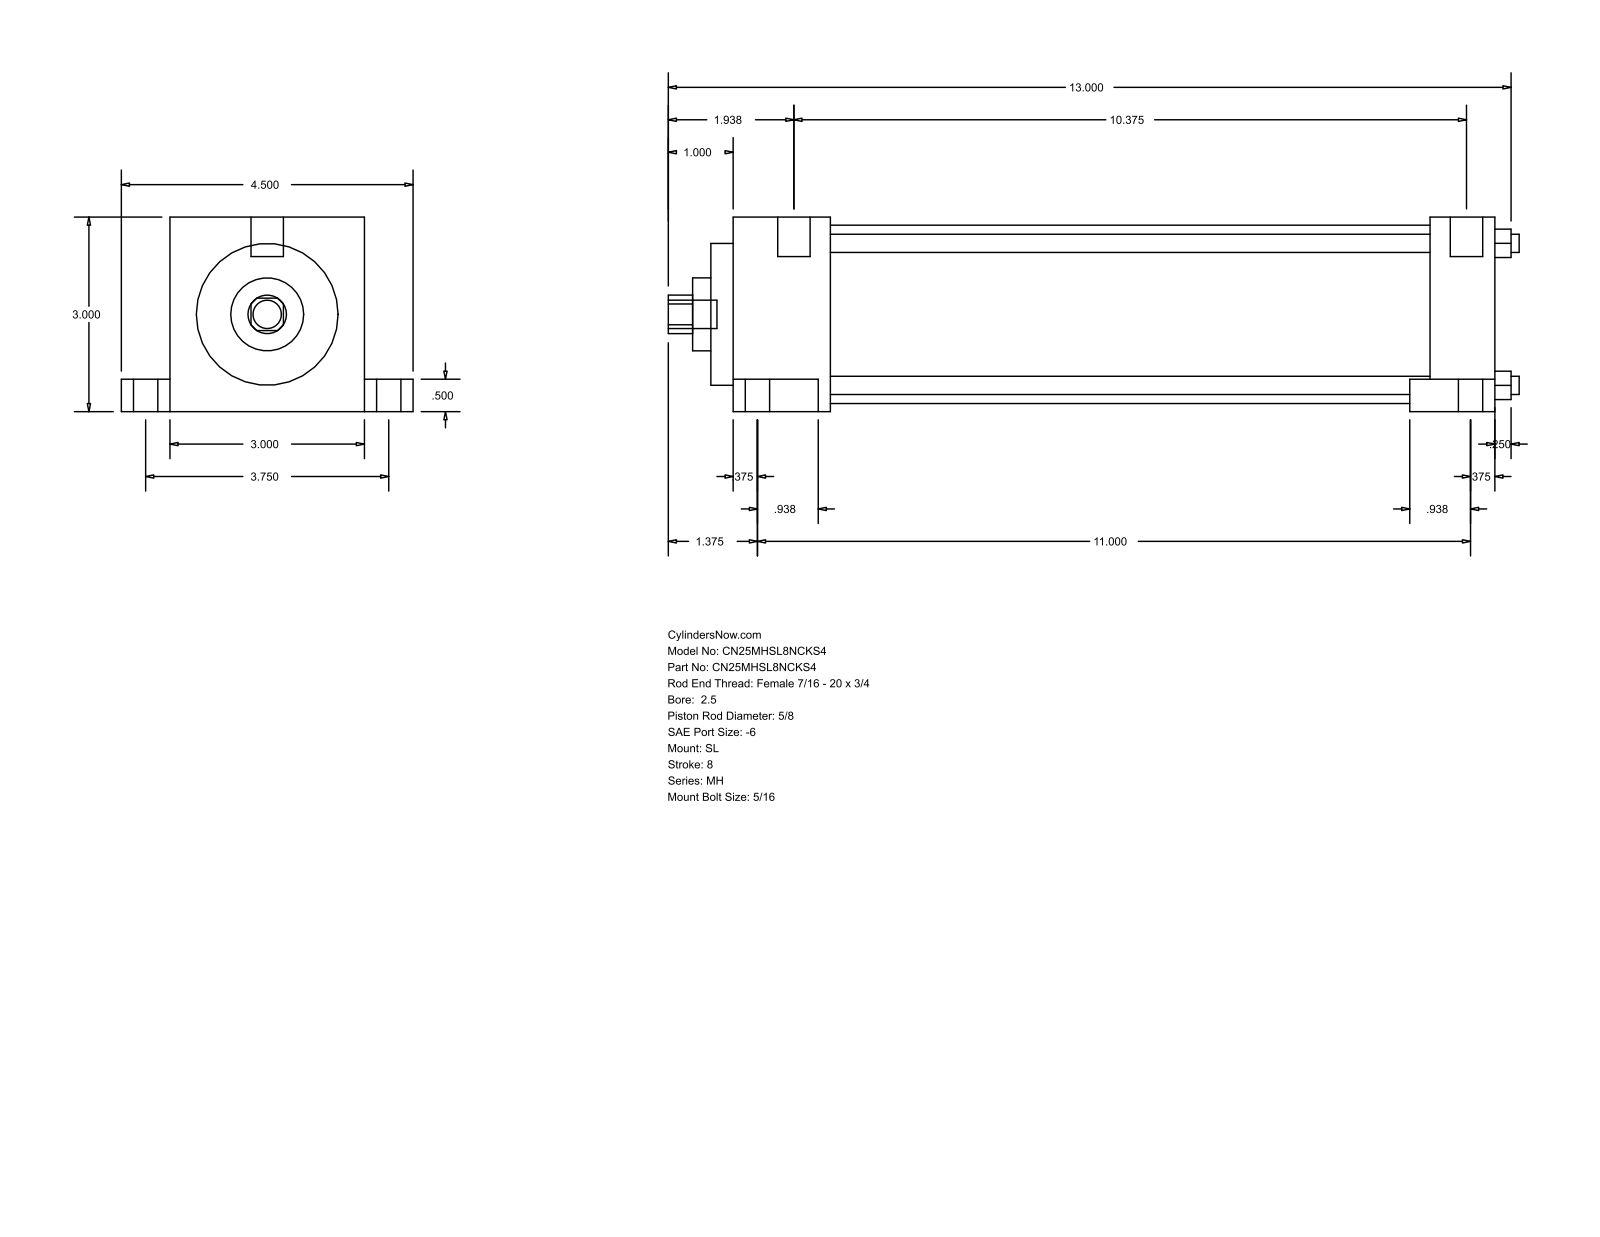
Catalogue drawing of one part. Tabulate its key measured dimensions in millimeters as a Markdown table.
| quantity | value |
| --- | --- |
| part name | MH_SL__0250_0.625 |
| STEP written by | GSSL Pune (CONFIG_CONTROL_DESIGN) |
| units | millimeters |
| bodies | 0 solids, 86 faces (61 planar, 25 cylindrical, 0 other) |
| overall size | 333.38 × 114.3 × 76.2 |
| round holes (diameter × count) | 7.14 × 4, 15.88 × 1, 28.57 × 1, 55.55 × 1, 69.85 × 1 |
| round bosses / shafts (diameter × count) | 15.88 × 2, 9.53 × 2, 5.56 × 2, 12.7 × 1, 11.11 × 1 |
| partial cylindrical surfaces (radius × count) | 7.54 × 1 |
| main face-to-face distances | 76.2, 25.4, 281.78, 307.18, 12.7, 63.5, 19.05, 95.25, 31.75, 273.84 |
| hole center spacings | 39.33, 55.62, 78.66 |
